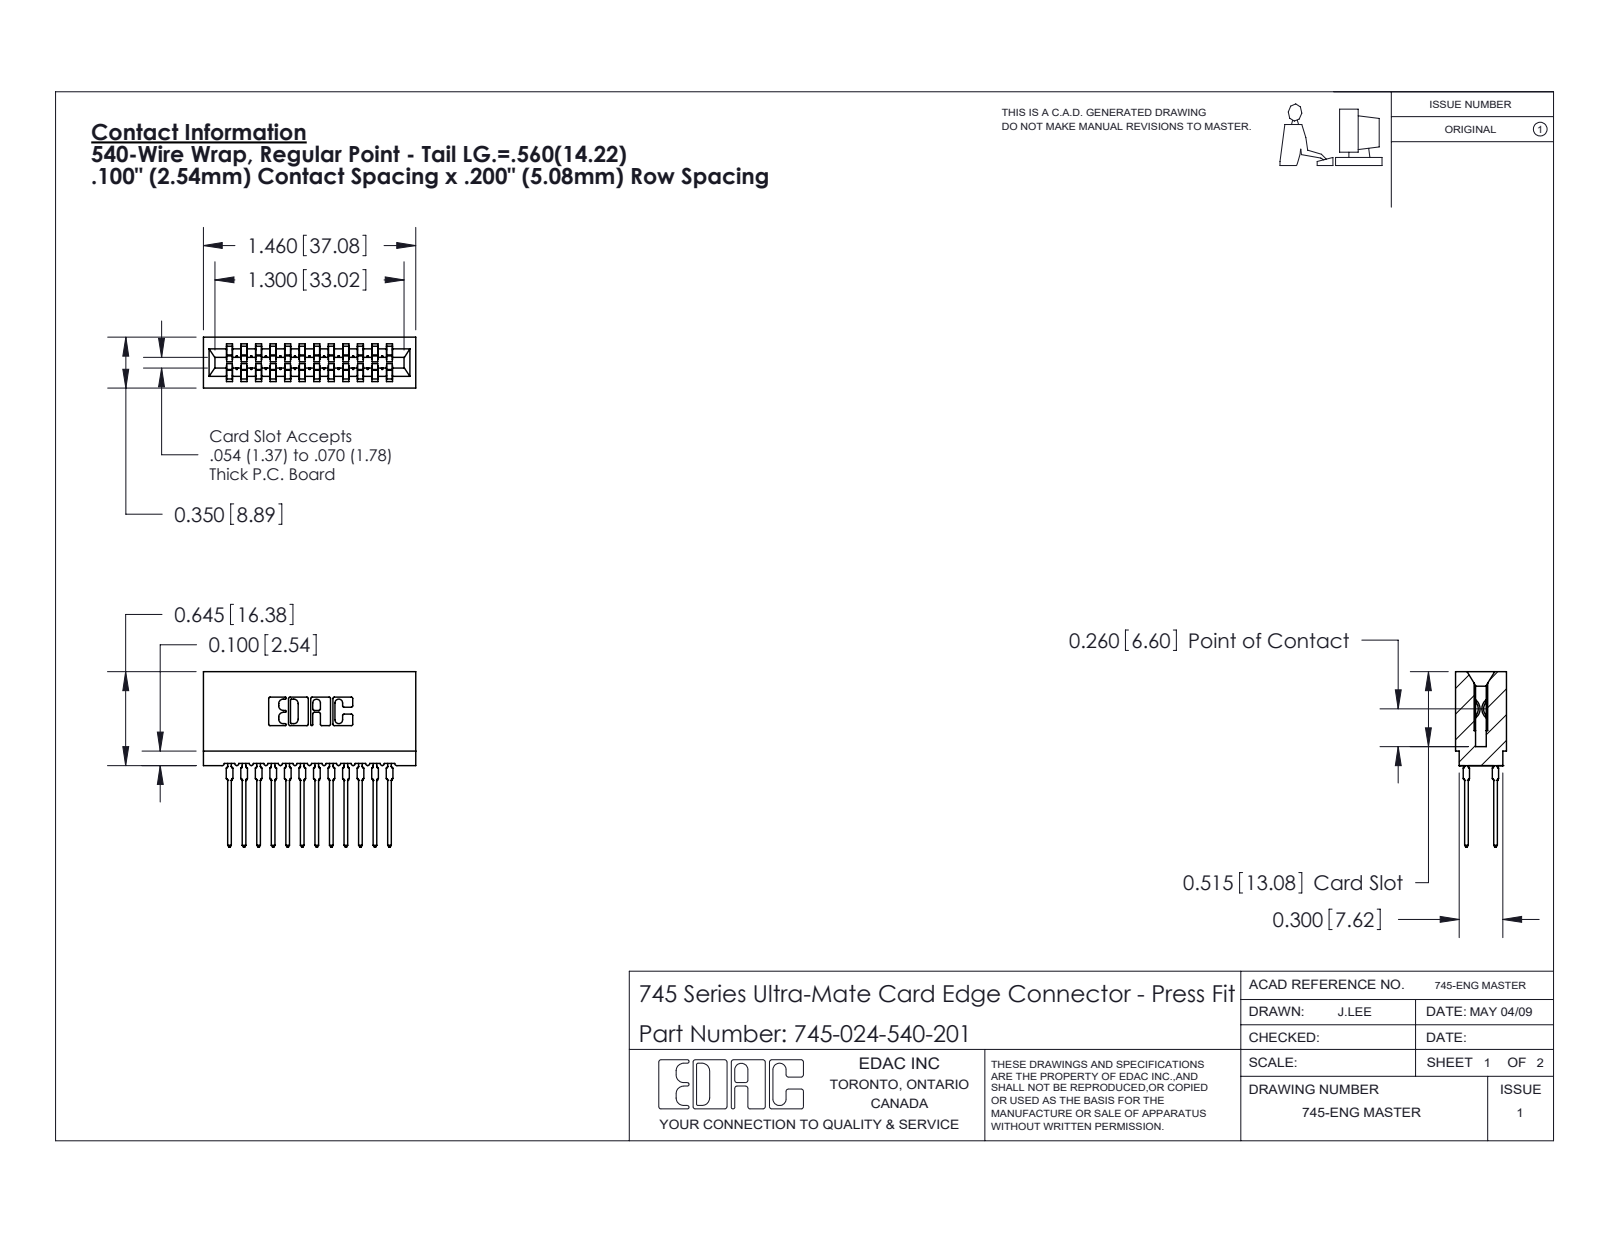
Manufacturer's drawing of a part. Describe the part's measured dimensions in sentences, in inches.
The part is named "745-024-540-201; 745 Part_Insulator Option - 01; 745-292-001_540". Its 3-D file was written by "SolidWorks 2020 (CONFIG_CONTROL_DESIGN)". It is 25 solids with 2243 faces: 1159 planar, 460 cylindrical and 624 other. Overall it measures 1.46 by 1.206 by 0.35 inches. Its volume is 0.219 cubic inches and its surface area 10.67 square inches. Partial cylindrical surfaces (rounded edges, fillets, slot ends): 48 of radius 0.021, 24 of radius 0.015, 22 of radius 0.01, 8 of radius 0.005, 8 of radius 0.011, 6 of radius 0.007, 6 of radius 0.031, 3 of radius 0.026. The main face-to-face distances are 0.2, 0.1, 0.3, 0.5, 0.4, 0.6, 0.063, 0.287, 0.35, 0.042.
